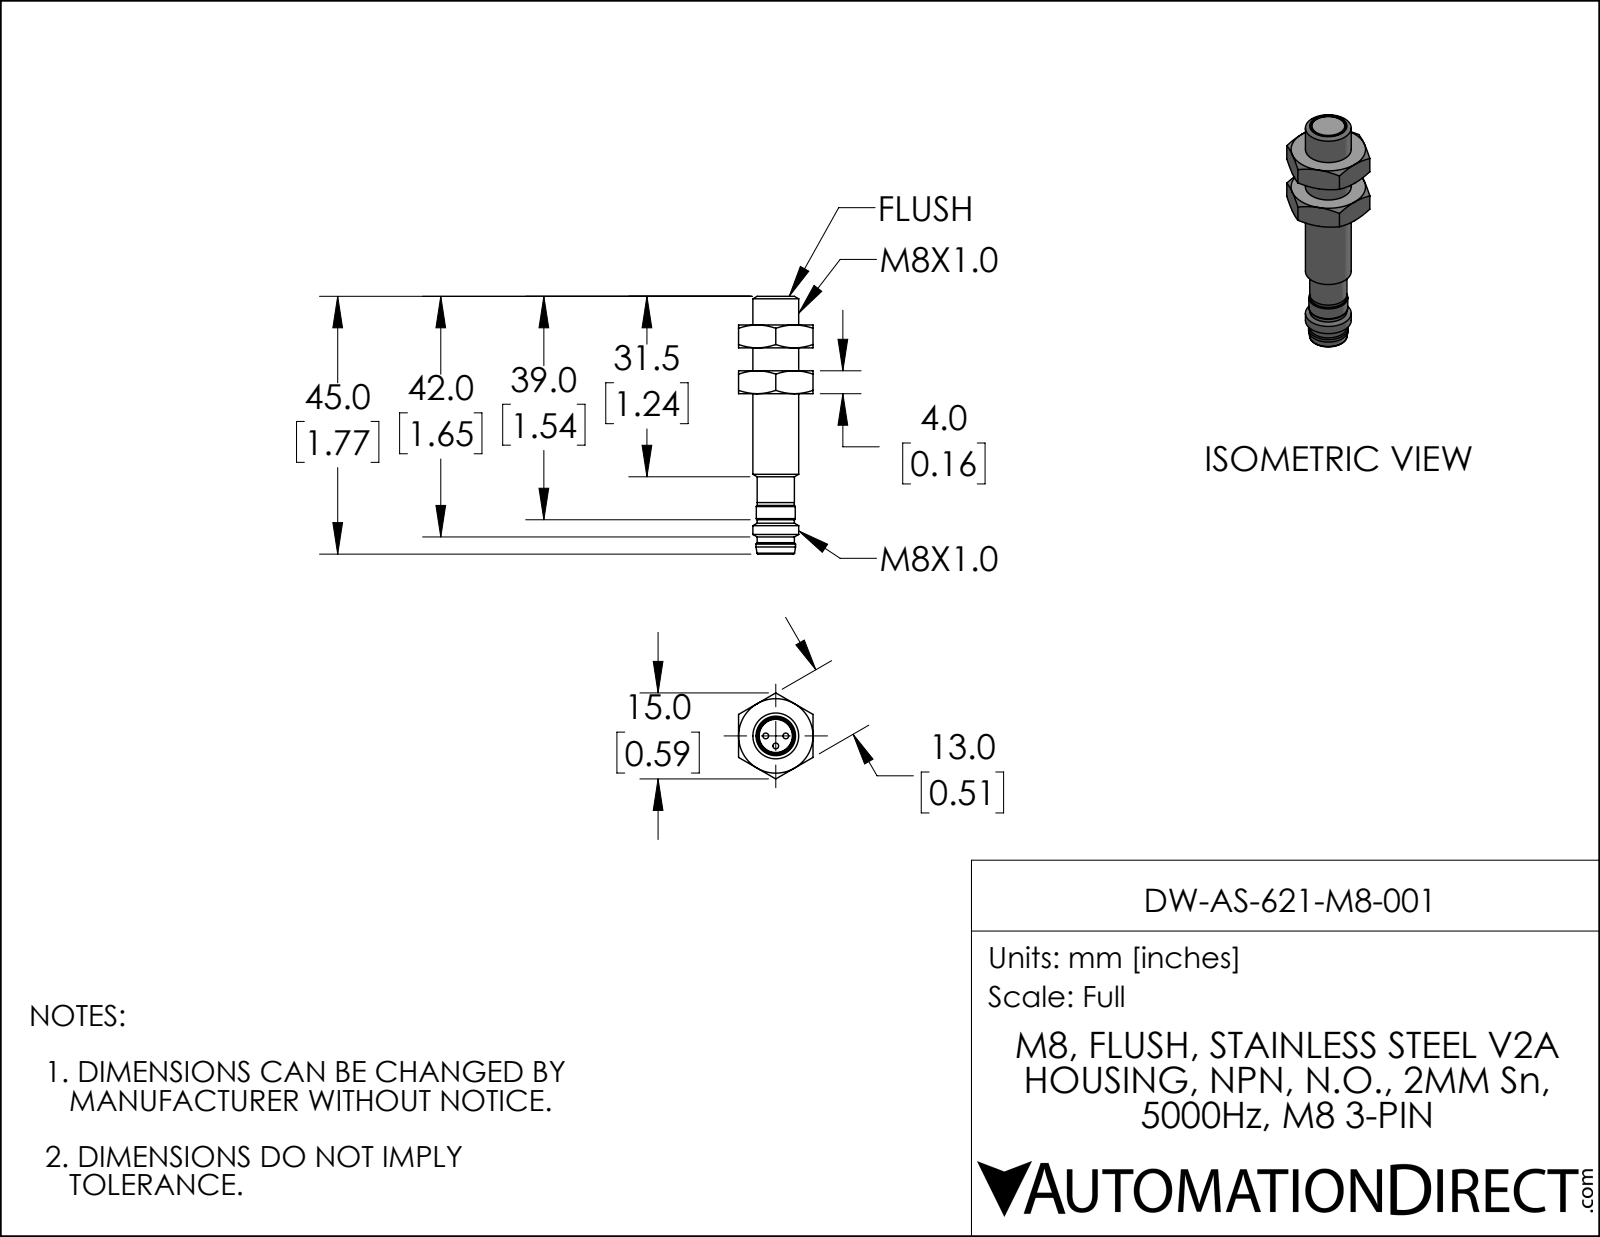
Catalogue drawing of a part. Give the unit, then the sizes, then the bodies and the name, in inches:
Units: inches
Overall size (bounding box): 1.772 × 0.591 × 0.512
Round holes (diameter × count): ⌀0.228 ×1
Round bosses / shafts (diameter × count): ⌀0.039 ×3, ⌀0.315 ×1, ⌀0.272 ×1, ⌀0.268 ×1, ⌀0.256 ×1, ⌀0.254 ×1
Main face-to-face distances: 0.157, 0.512, 0.315, 0.472, 0.197, 0.354, 0.669, 1.575, 1.22, 1.063
Volume: 0.165 in³ · Surface area: 2.85 in²
Bodies: 1 solid, 77 faces (25 planar, 14 cylindrical, 38 other)
Part name (STEP PRODUCT): DW-AS-621-M8-001
STEP written by: SolidWorks 2019 (AUTOMOTIVE_DESIGN)
